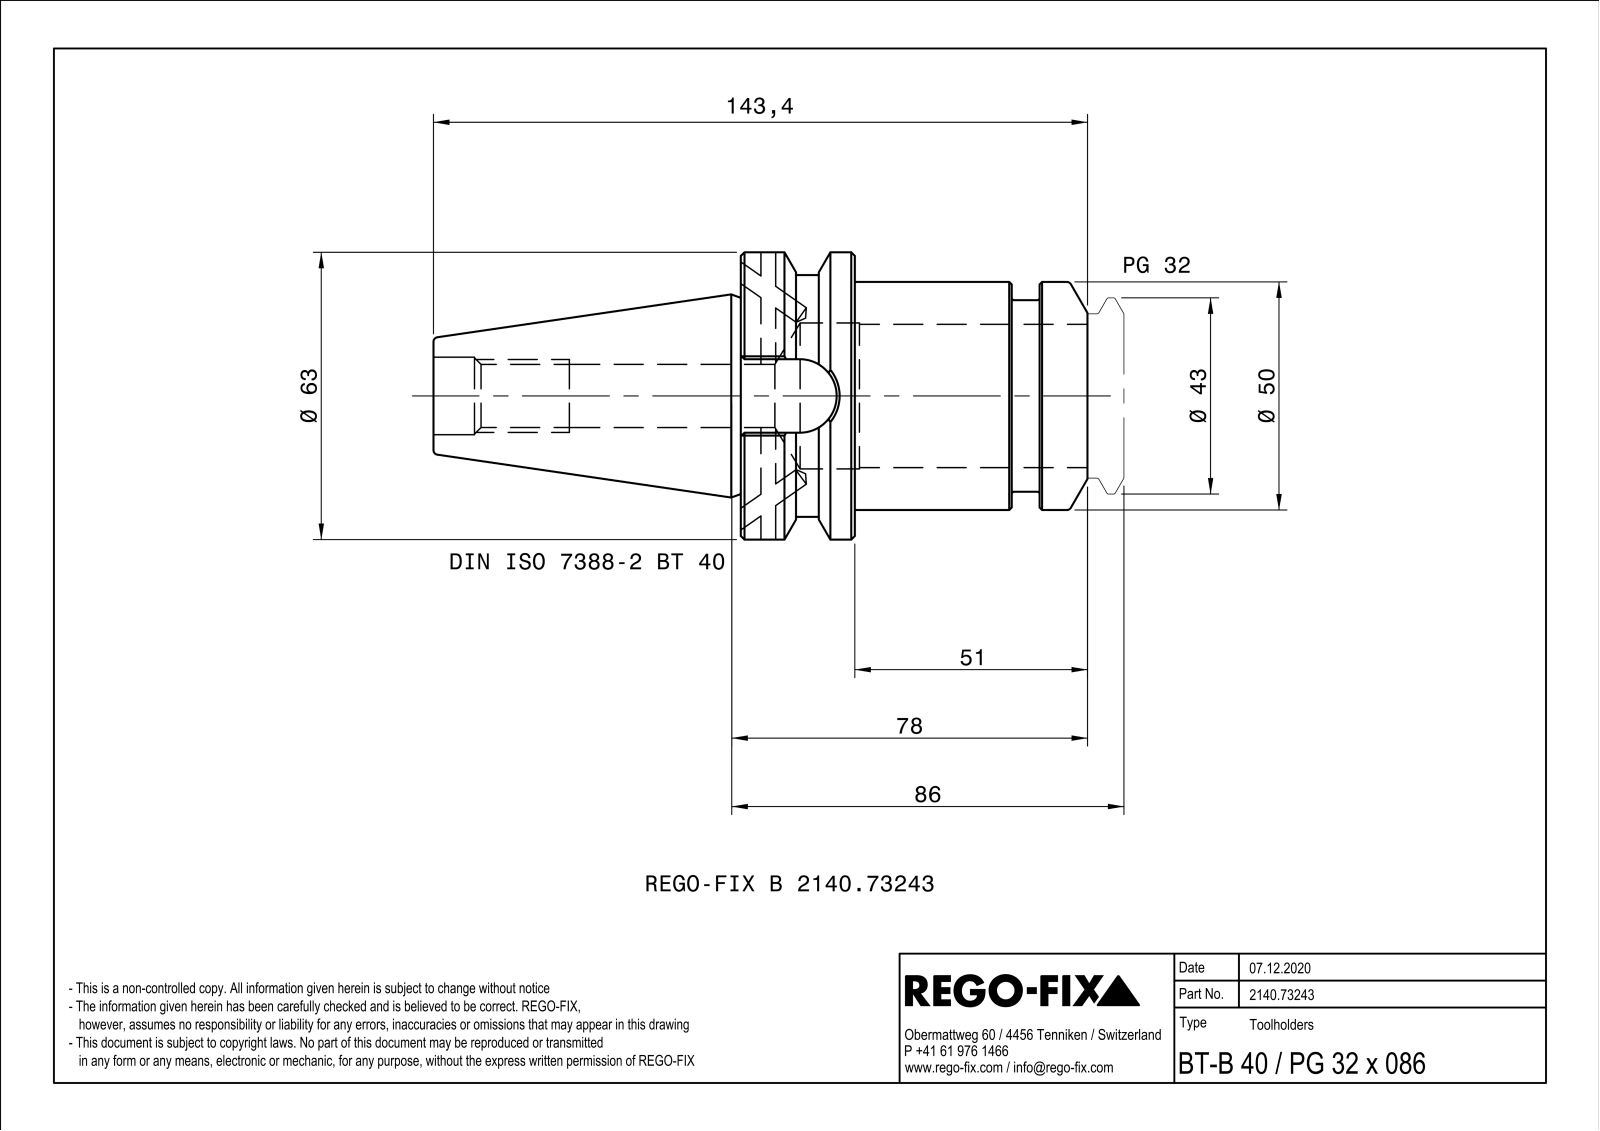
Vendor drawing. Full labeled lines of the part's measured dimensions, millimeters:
Part name (STEP PRODUCT): NOCUT
STEP written by: SIEMENS PLM Software Solid Edge ST10 (AUTOMOTIVE_DESIGN)
Units: millimetres
Bodies: 1 solid, 98 faces (39 planar, 26 cylindrical, 33 other)
Overall size (bounding box): 143.4 × 63 × 63
Volume: 163 606 mm³ · Surface area: 37 016 mm²
Round holes (diameter × count): ⌀3.24 ×2, ⌀3.9 ×2, ⌀13.84 ×1, ⌀17 ×1, ⌀33 ×1
Round bosses / shafts (diameter × count): ⌀63 ×1, ⌀53 ×1, ⌀50 ×1, ⌀42 ×1
Partial cylindrical surfaces — rounded edges, fillets, slot ends (radius × count): R0.5 ×4, R8.05 ×1
Main face-to-face distances: 25, 34.4, 59.4, 6.1, 40.5, 65.5, 45.1, 10.5, 16.6, 51
